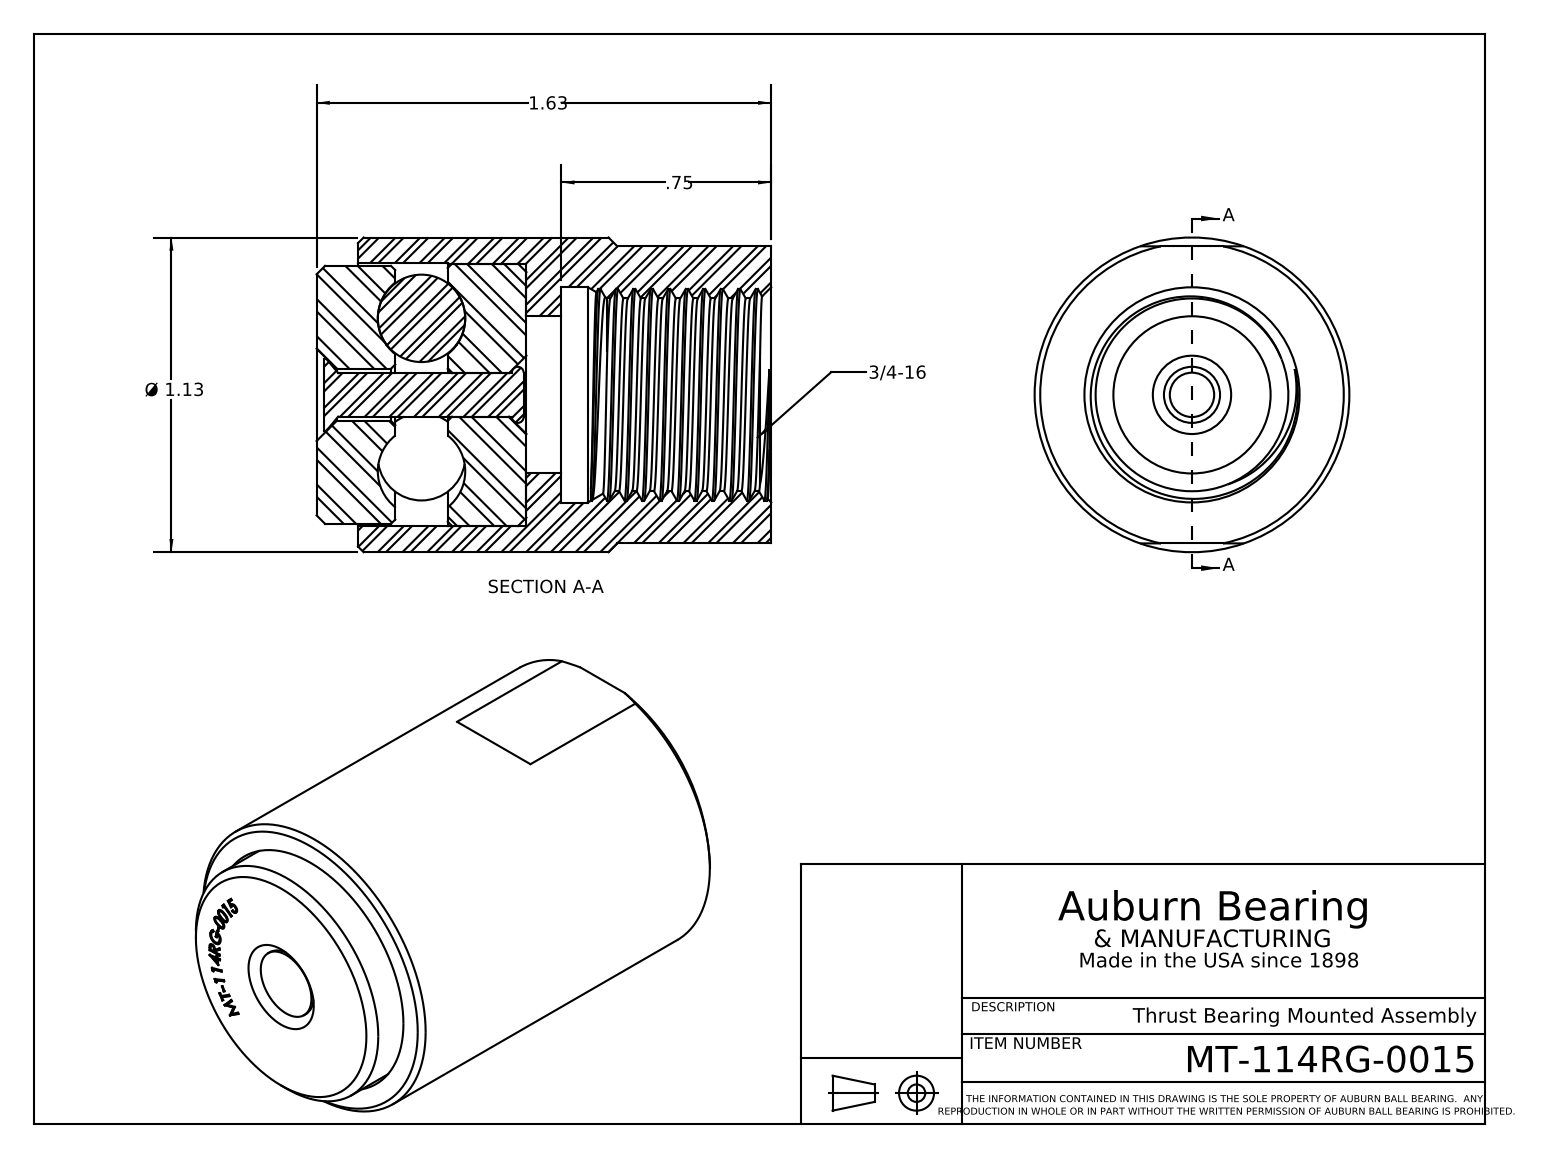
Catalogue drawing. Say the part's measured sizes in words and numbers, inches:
The part is named "MT-114RG-0015". Its 3-D file was written by "SolidWorks 2020 (CONFIG_CONTROL_DESIGN)". It is 9 solids with 245 faces: 116 planar, 41 cylindrical and 88 other. Overall it measures 1.625 by 1.125 by 1.125 inches. Its volume is 1.117 cubic inches and its surface area 17.72 square inches. Round holes: 1 of diameter 0.156, 1 of diameter 0.187, 1 of diameter 0.562, 1 of diameter 0.689, 1 of diameter 0.77, 1 of diameter 0.937, 1 of diameter 0.94. Round bosses or shafts: 1 of diameter 1.125, 1 of diameter 0.937, 1 of diameter 0.922, 1 of diameter 0.256. The main face-to-face distances are 0.75, 0.875, 1.625, 0.148, 0.602, 1.477, 0.727, 0.125, 1.062, 0.469.
